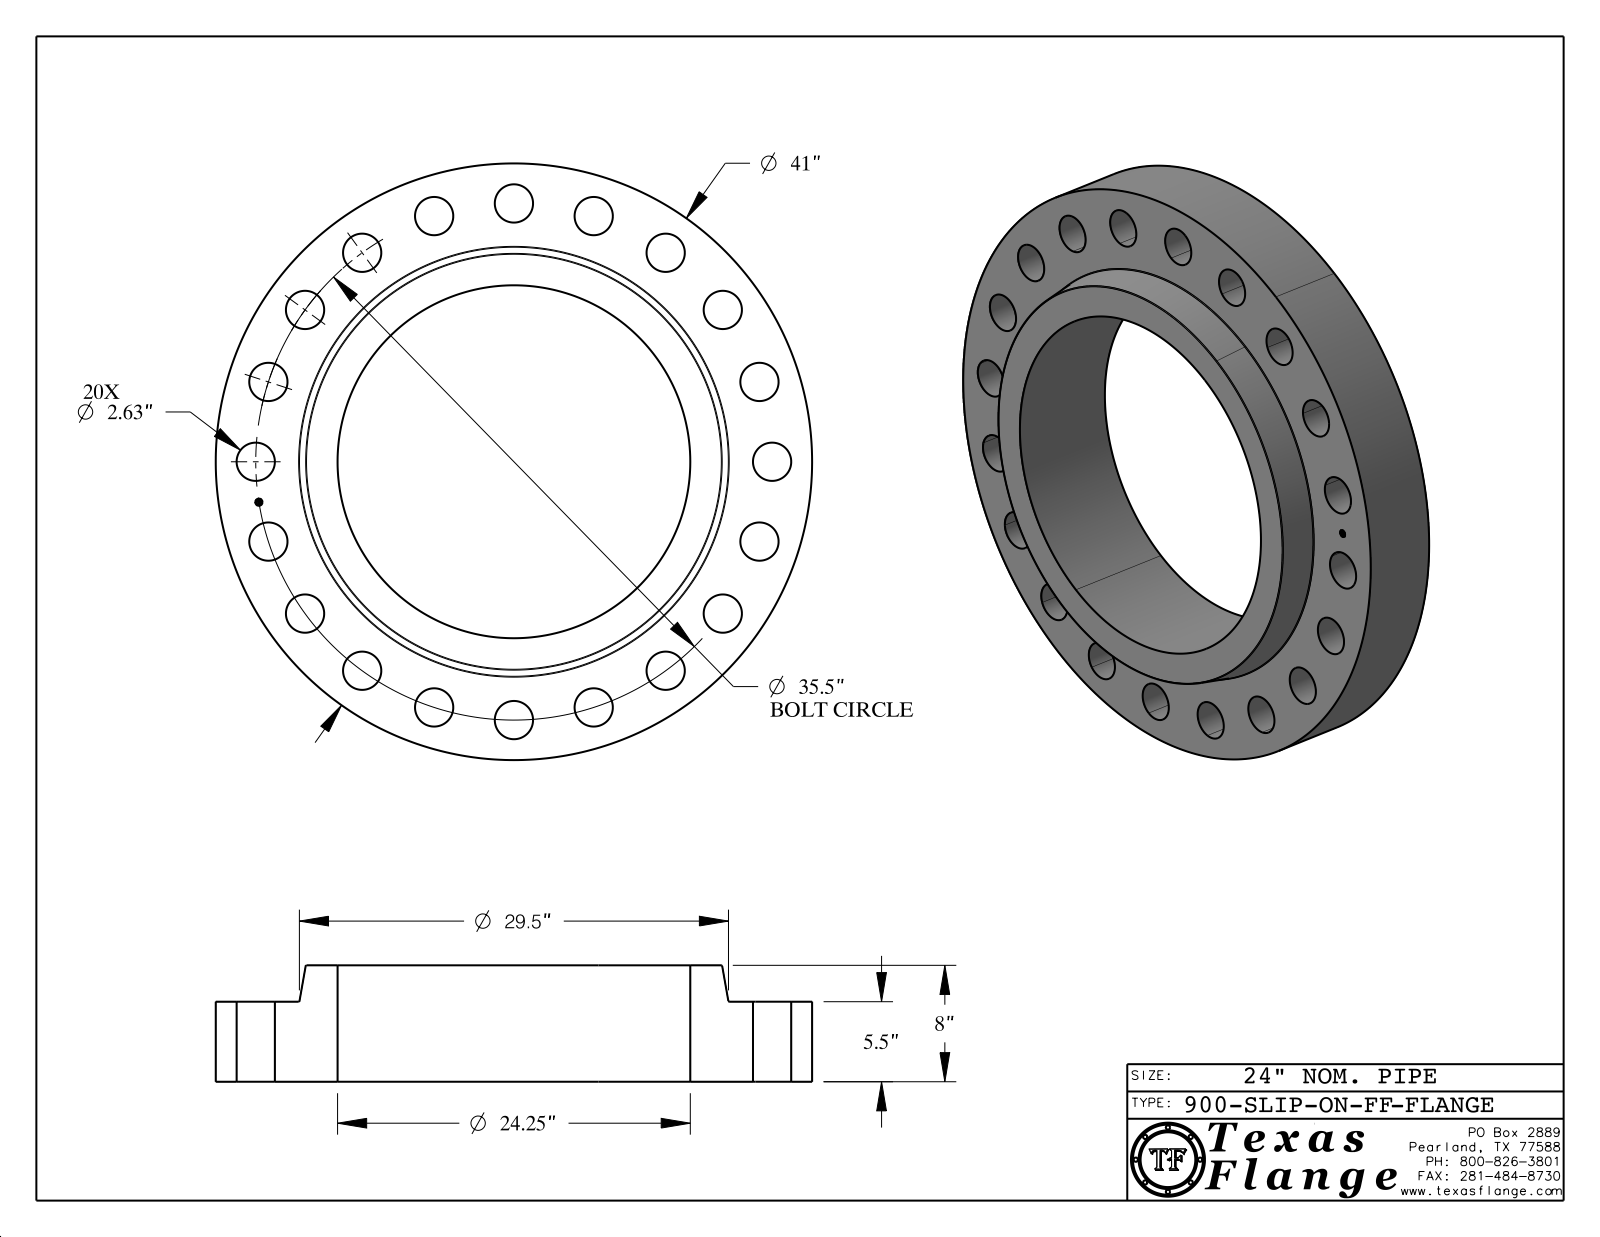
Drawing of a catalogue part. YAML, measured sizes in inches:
part_name: "900-SLIP-ON-FF"
step_written_by: "CATIA V5 STEP AP214 (AUTOMOTIVE_DESIGN)"
units: inches
bodies: {solids: 1, faces: 438, planar: 368, cylindrical: 64, other: 6}
overall_size: [41, 41, 8]
volume: 4627
surface_area: 3915
round_holes:
  - {diameter: 2.63, count: 20}
  - {diameter: 0.495, count: 1}
  - {diameter: 24.25, count: 1}
round_bosses_or_shafts:
  - {diameter: 0.03, count: 8}
  - {diameter: 41, count: 1}
  - {diameter: 0.39, count: 1}
face_to_face_distances: [5.5, 8, 2.5, 5.485, 0.015, 2.515, 0.148, 0.144, 0.027, 0.096]
hole_center_spacings: [17.75, 10.97, 28.72, 31.631, 16.117, 20.866, 25.102, 33.762]
